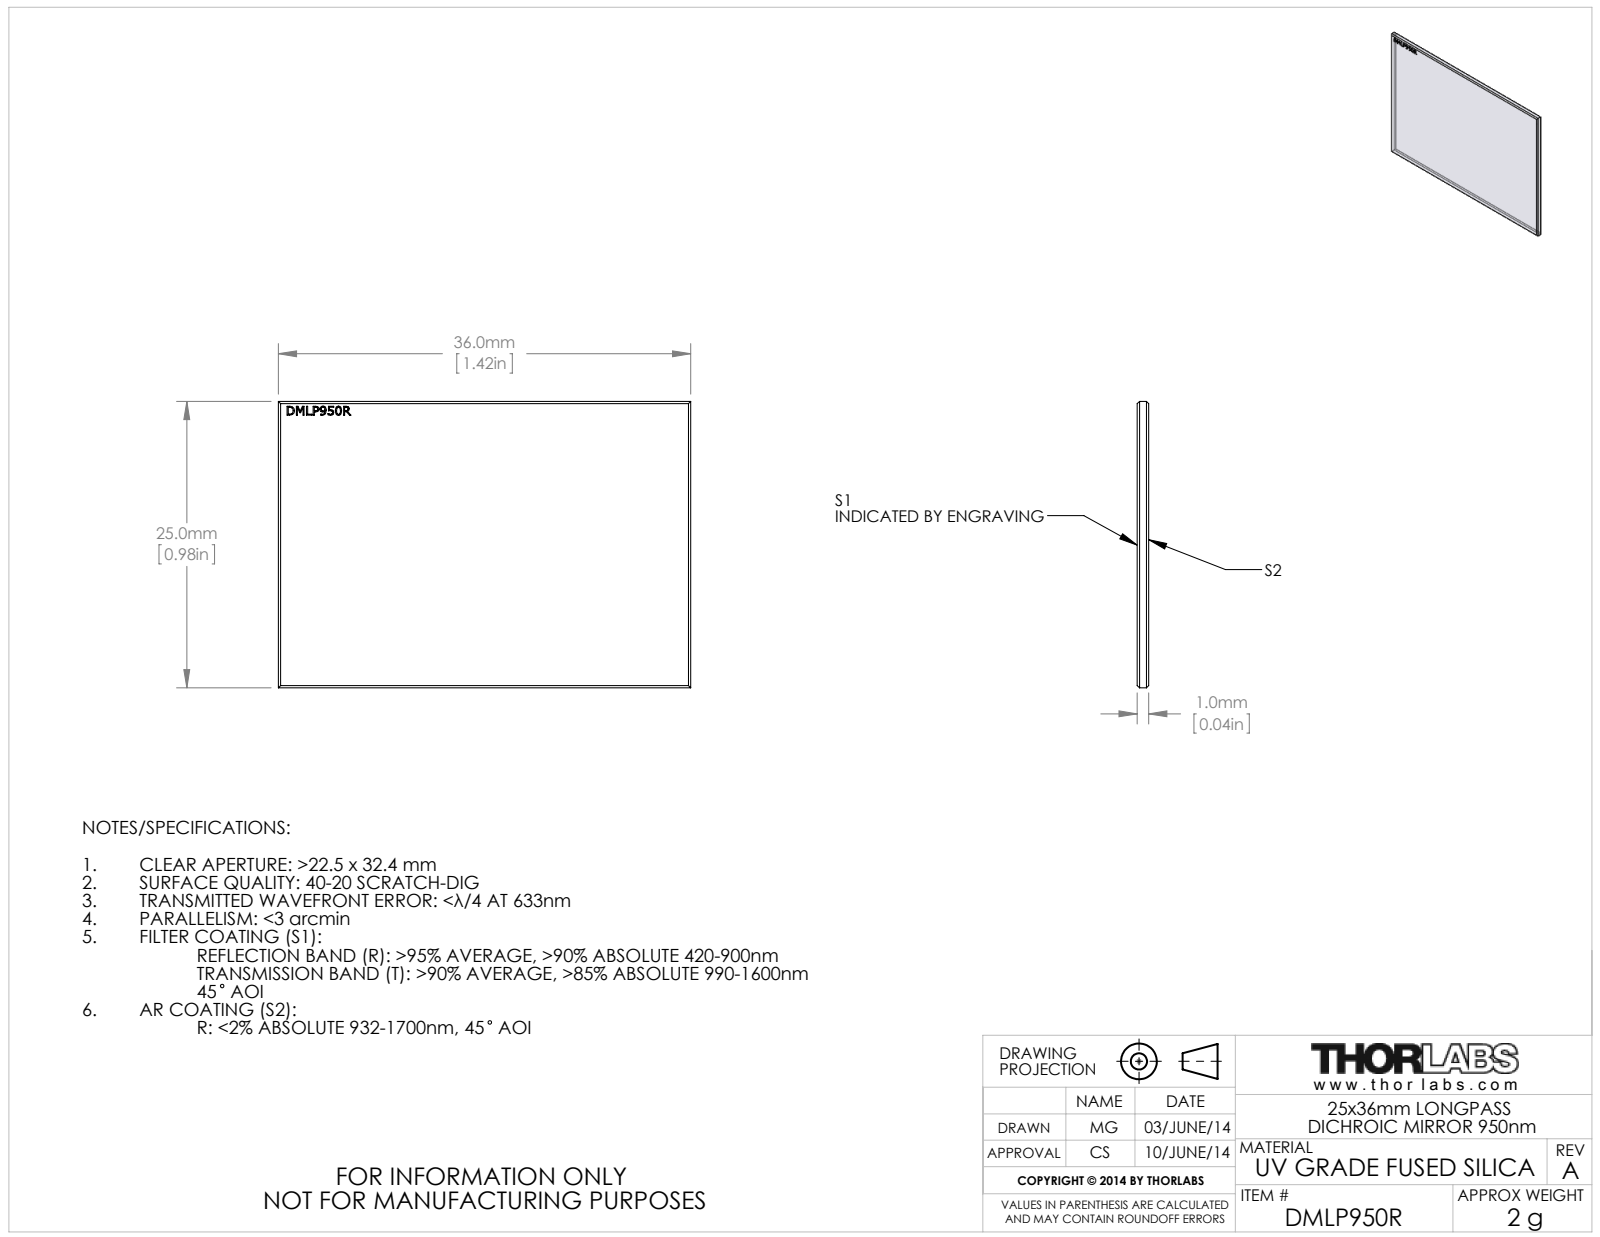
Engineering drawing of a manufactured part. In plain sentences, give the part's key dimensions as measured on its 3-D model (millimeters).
The part is named "TTN028303-E0W". Its 3-D file was written by "SolidWorks 2012 (CONFIG_CONTROL_DESIGN)". It is 1 solid with 145 faces: 80 planar, 0 cylindrical and 65 other. Overall it measures 36 by 25 by 1 millimeters. Its volume is 895 cubic millimeters and its surface area 1 893 square millimeters. The main face-to-face distances are 1, 25, 18.1, 36, 25.88, 0.9, 0.59, 0.81, 24.57, 0.43.
